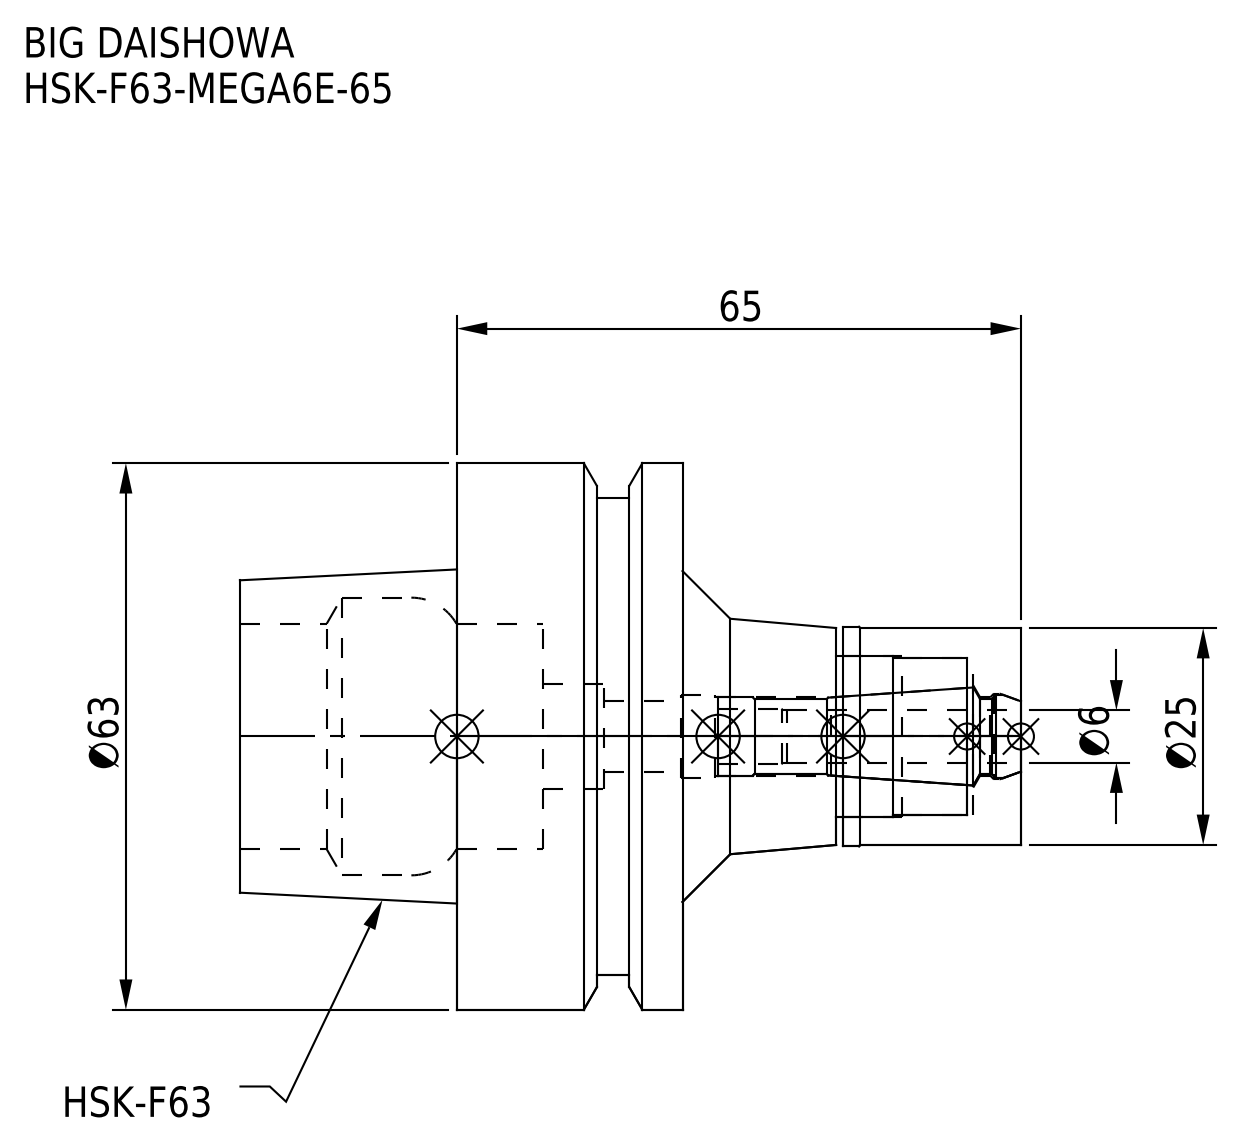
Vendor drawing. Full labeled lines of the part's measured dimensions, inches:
Part name (STEP PRODUCT): HF63ME06065-060_ASM.stp; HSK-F63-MEGA6E-65-060-FreeParts; DXF_TEMP_ASSY_ASM_4_ASM.stp; HSK-F63-MEGA6E-65 (+3 more)
STEP written by: SolidWorks 2019 (CONFIG_CONTROL_DESIGN)
Units: inches
Bodies: 2 solids, 78 faces (16 planar, 38 cylindrical, 24 other)
Overall size (bounding box): 3.543 × 2.48 × 2.48
Volume: 6.104 in³ · Surface area: 39.28 in²
Round holes (diameter × count): ⌀0.325 ×1, ⌀0.354 ×1, ⌀0.378 ×1, ⌀0.39 ×1, ⌀0.472 ×1, ⌀0.709 ×1, ⌀0.728 ×1, ⌀1.024 ×1, ⌀1.26 ×1
Round bosses / shafts (diameter × count): ⌀2.48 ×1, ⌀2.165 ×1, ⌀0.996 ×1, ⌀0.984 ×1
Main face-to-face distances: 1.024, 2.008, 0.984, 1.535, 2.559, 3.543, 2.167, 0.632, 0.392, 1.376
